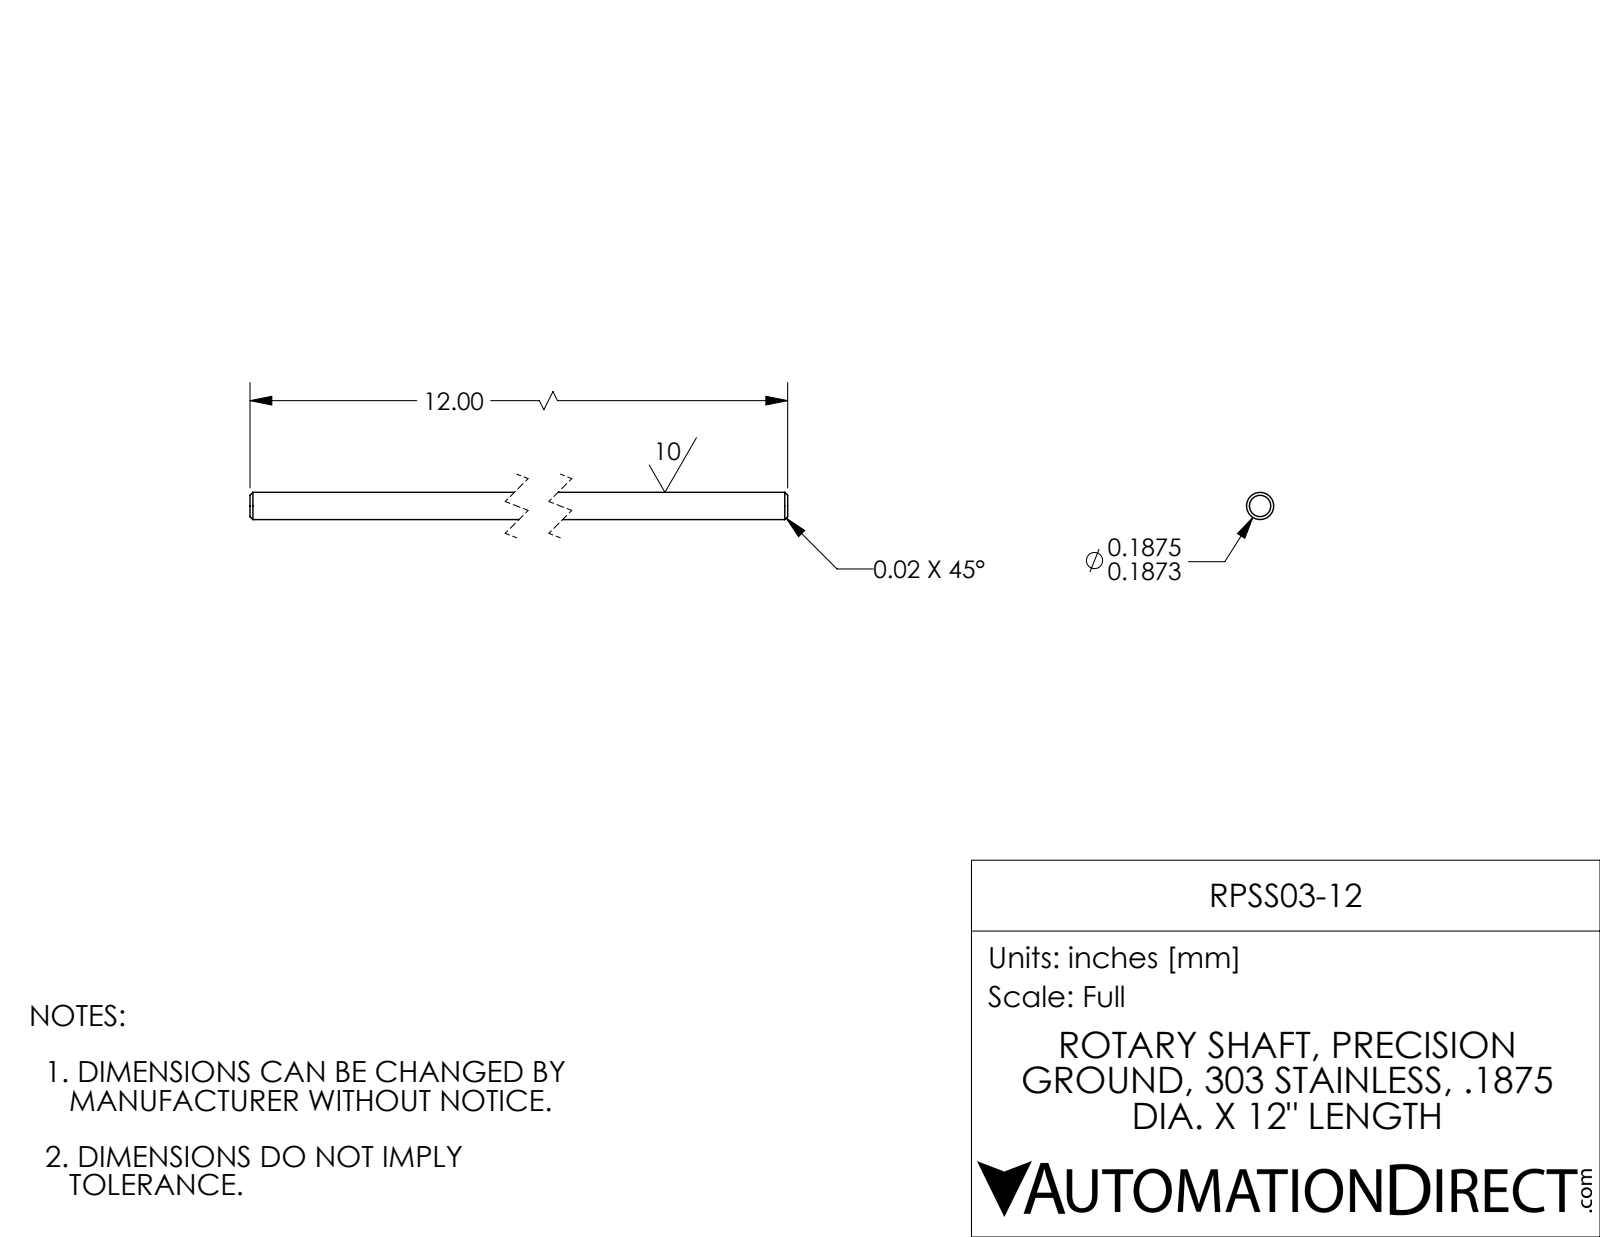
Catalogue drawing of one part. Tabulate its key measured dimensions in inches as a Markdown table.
| quantity | value |
| --- | --- |
| part name | RPSS03-12 |
| STEP written by | SolidWorks 2017 (AUTOMOTIVE_DESIGN) |
| units | inches |
| bodies | 1 solid, 8 faces (2 planar, 2 cylindrical, 4 other) |
| overall size | 12 × 0.188 × 0.188 |
| volume | 0.331 in³ |
| surface area | 7.109 in² |
| round bosses / shafts (diameter × count) | 0.187 × 1 |
| main face-to-face distances | 12 |
